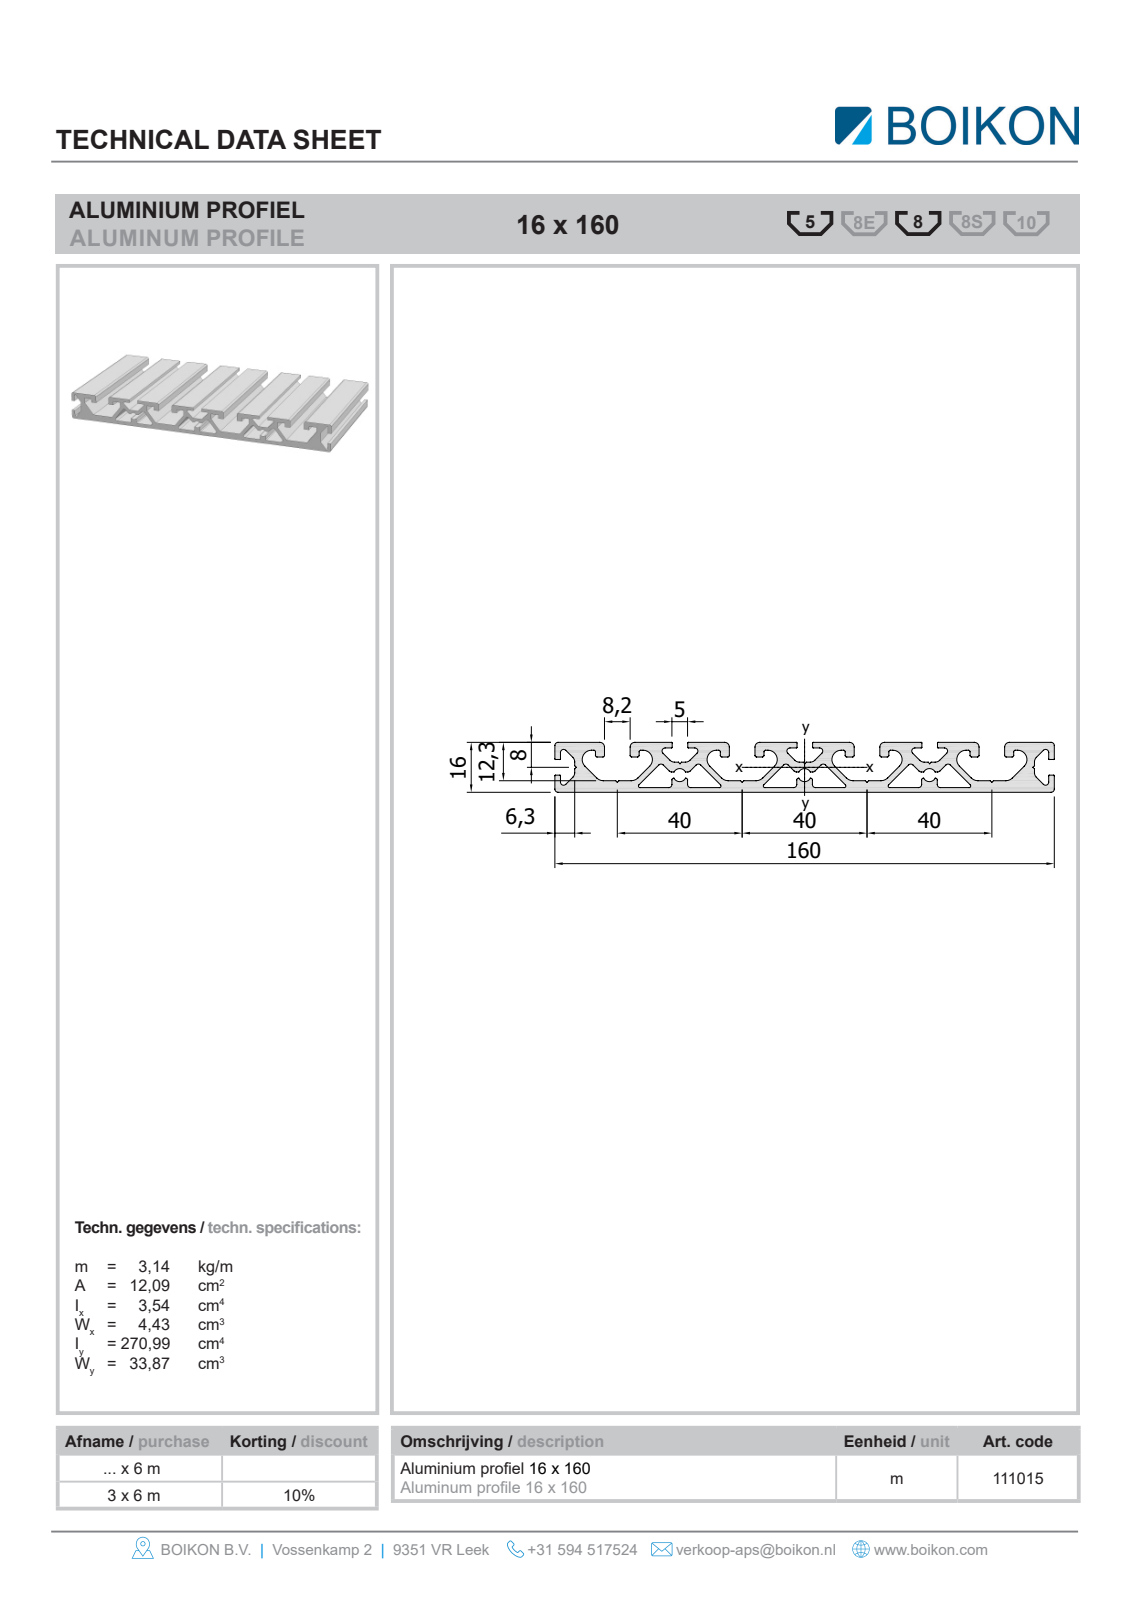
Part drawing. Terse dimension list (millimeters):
name: Root; 11101516x160BOIKON0
written by: HiCAD 2013 1802.4 Build 509 (AUTOMOTIVE_DESIGN)
unit: mm
bodies: 1 solid, 124 faces (102 planar, 22 cylindrical, 0 other)
size: 1000 × 160 × 16
volume: 1 505 000 mm³; area: 687 698 mm²
rounds: 12× R1, 10× R0.5
face distances: 16, 31.2, 1.8, 3.75, 12.25, 4.5, 13.6, 9.85, 2.4, 62.4
